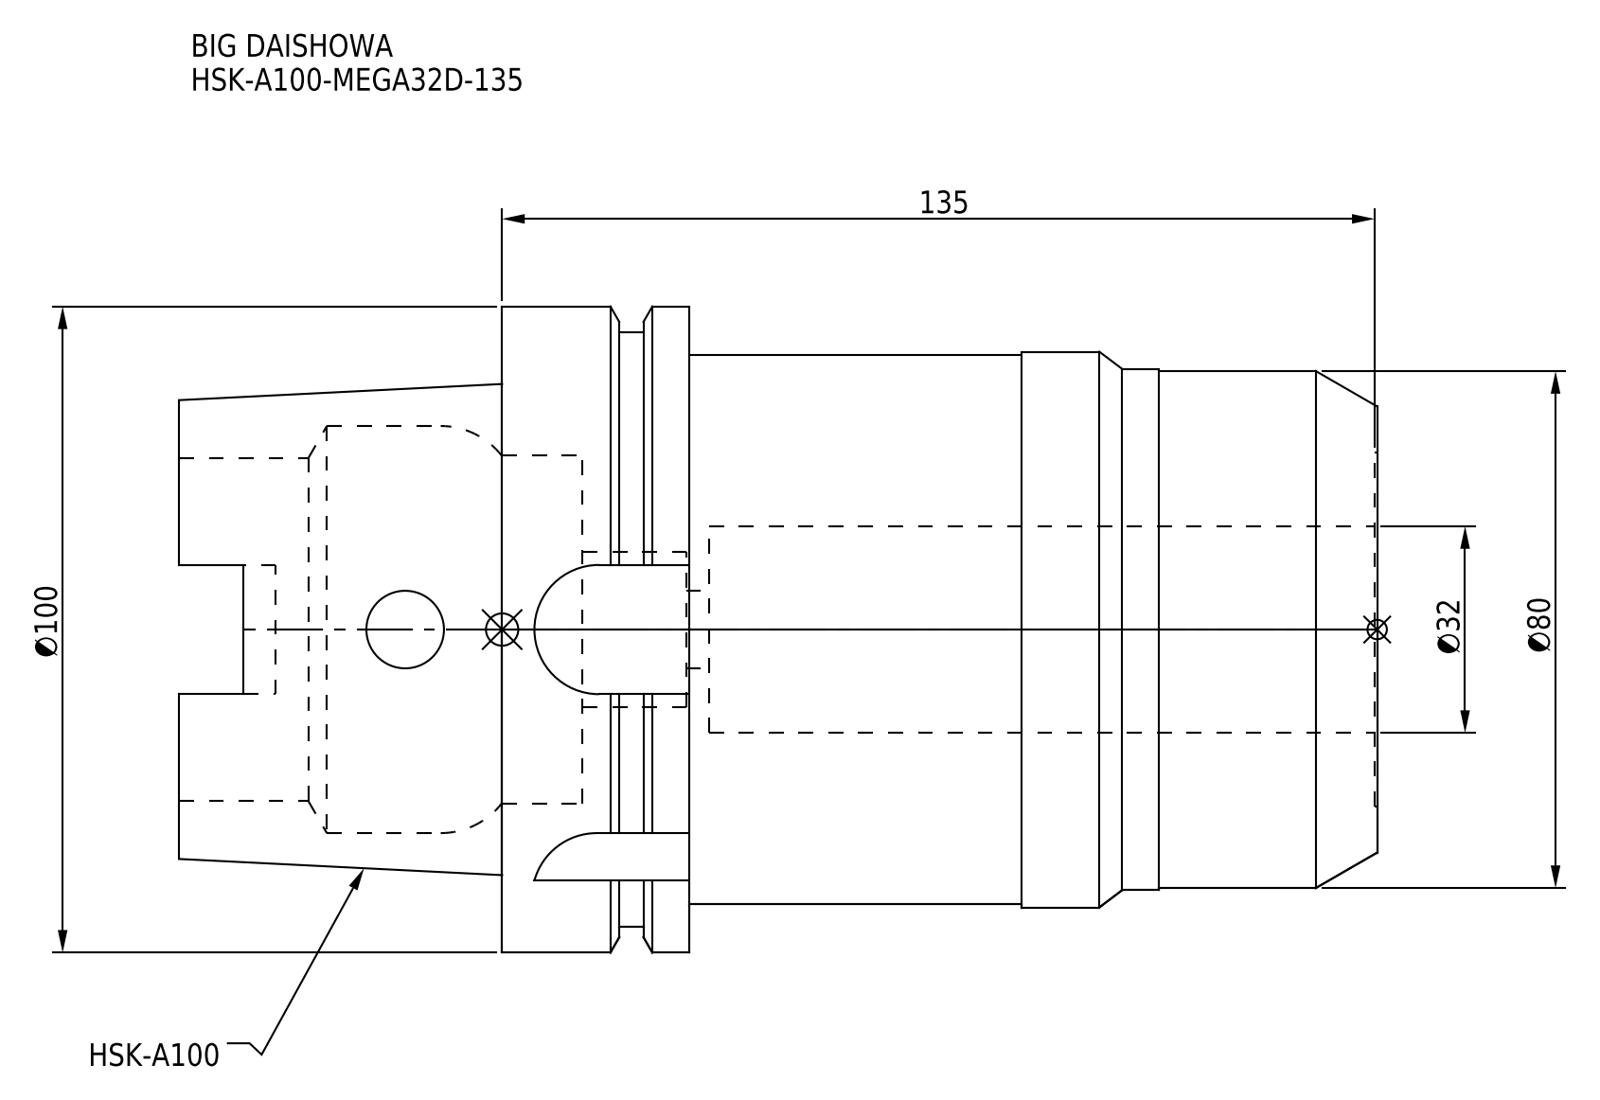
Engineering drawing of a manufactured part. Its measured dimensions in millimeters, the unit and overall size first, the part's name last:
Units: millimetres
Overall size (bounding box): 185.4 × 100 × 100
Round holes (diameter × count): ⌀12 ×2, ⌀24 ×1, ⌀32 ×1, ⌀53 ×1, ⌀53.8 ×1, ⌀54.7 ×1, ⌀63 ×1
Round bosses / shafts (diameter × count): ⌀100 ×1, ⌀92 ×1, ⌀86 ×1, ⌀85 ×1, ⌀80.7 ×1, ⌀80 ×1
Partial cylindrical surfaces — rounded edges, fillets, slot ends (radius × count): R4.88 ×4, R10 ×4
Main face-to-face distances: 29, 16.55, 12.45, 106, 122.55, 135, 0.4, 106.4, 122.95, 135.4
Volume: 742 605 mm³ · Surface area: 86 853 mm²
Bodies: 1 solid, 98 faces (36 planar, 44 cylindrical, 18 other)
Part name (STEP PRODUCT): HSK-A100-MEGA32D-135
STEP written by: CREO PARAMETRIC BY PTC INC, 2016380 (AUTOMOTIVE_DESIGN)
